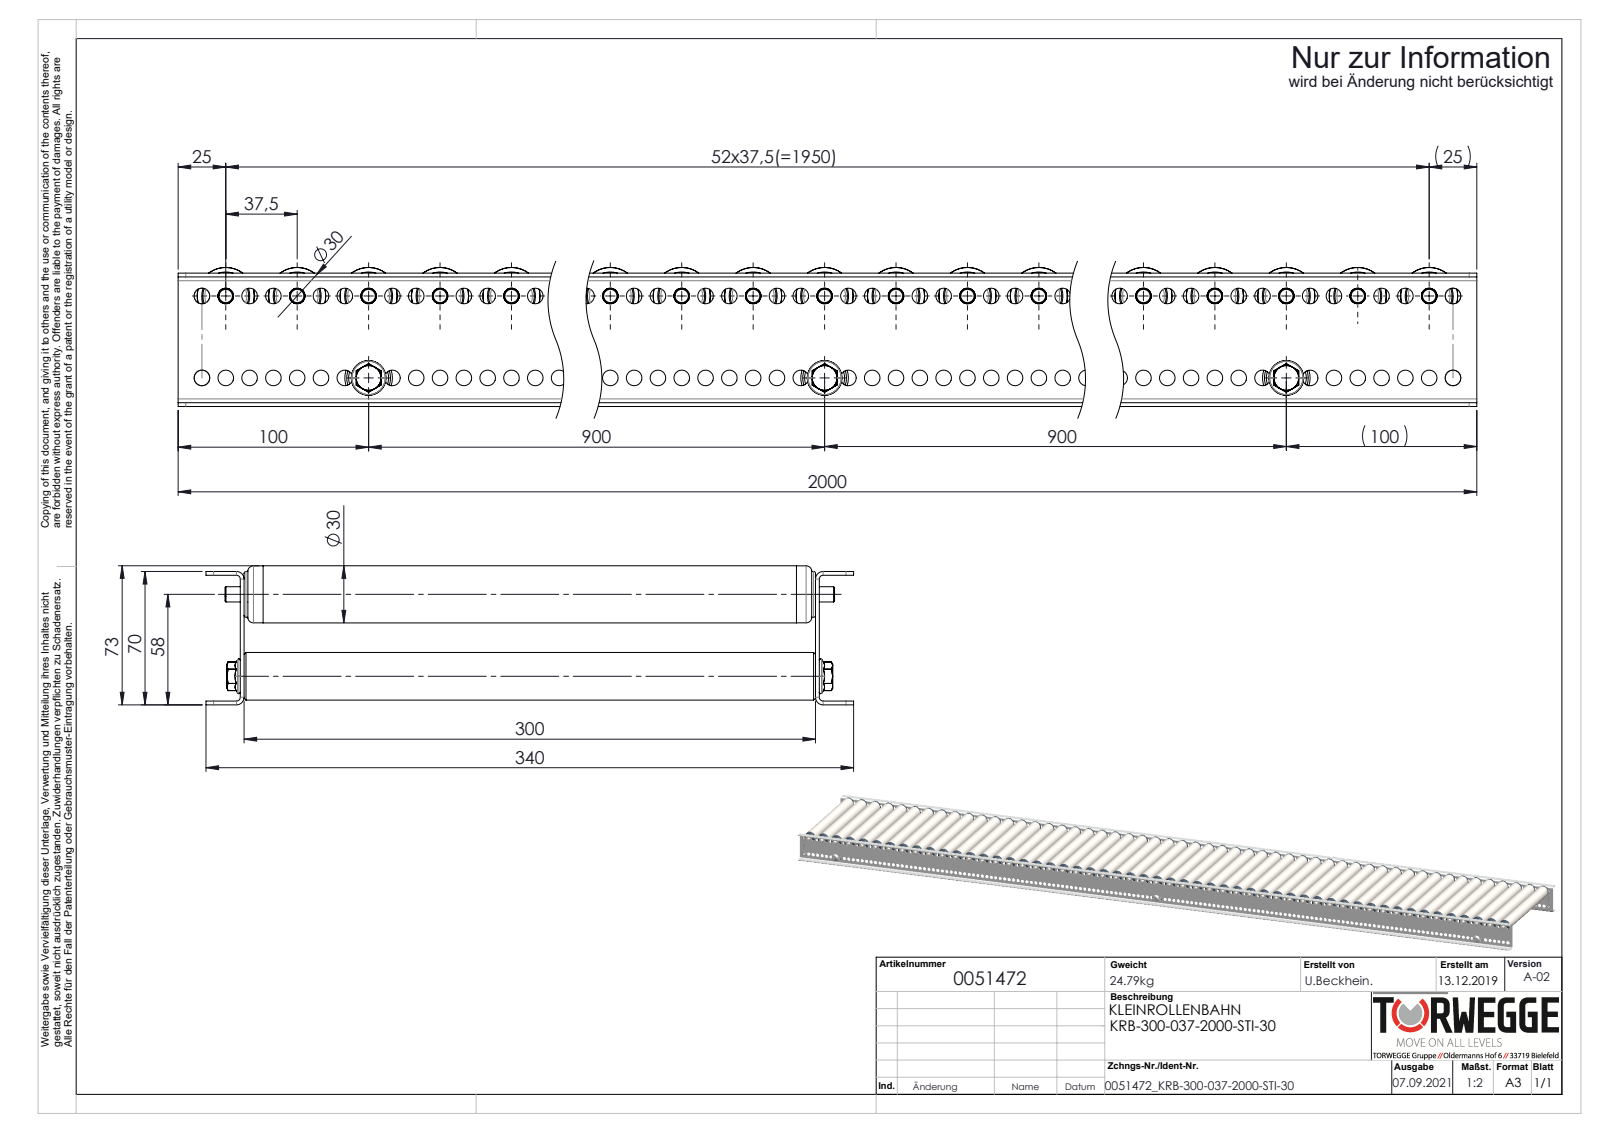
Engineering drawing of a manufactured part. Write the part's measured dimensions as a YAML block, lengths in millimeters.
part_name: "Traversen_KFG_L300; 0042503_Typ-KUT50-30x1,5-A8; 0051472; 0040250_DRUCK-FEDER-8mm (+6 more)"
step_written_by: "SolidWorks 2020 (AUTOMOTIVE_DESIGN)"
units: millimeters
bodies: {solids: 335, faces: 14068, planar: 4402, cylindrical: 5588, other: 4078}
overall_size: [2000, 340, 73]
volume: 3810000
surface_area: 4808000
round_holes:
  - {diameter: 8.2, count: 318}
  - {diameter: 8, count: 53}
  - {diameter: 8.1, count: 53}
  - {diameter: 23.2, count: 53}
  - {diameter: 25.2, count: 53}
  - {diameter: 27, count: 53}
  - {diameter: 6.8, count: 3}
  - {diameter: 21, count: 3}
round_bosses_or_shafts:
  - {diameter: 30, count: 53}
  - {diameter: 29.9, count: 53}
  - {diameter: 27.1, count: 53}
  - {diameter: 26.8, count: 53}
  - {diameter: 24, count: 53}
  - {diameter: 14, count: 53}
  - {diameter: 25, count: 3}
  - {diameter: 8, count: 3}
partial_cylinders:
  - {radius: 5.05, count: 53}
  - {radius: 4, count: 8}
  - {radius: 2, count: 4}
face_to_face_distances: [2, 302, 300, 68, 304, 70, 66, 10, 290, 20]
hole_center_spacings: [12.5, 25, 37.5, 50, 62.5, 75, 87.5, 100]
